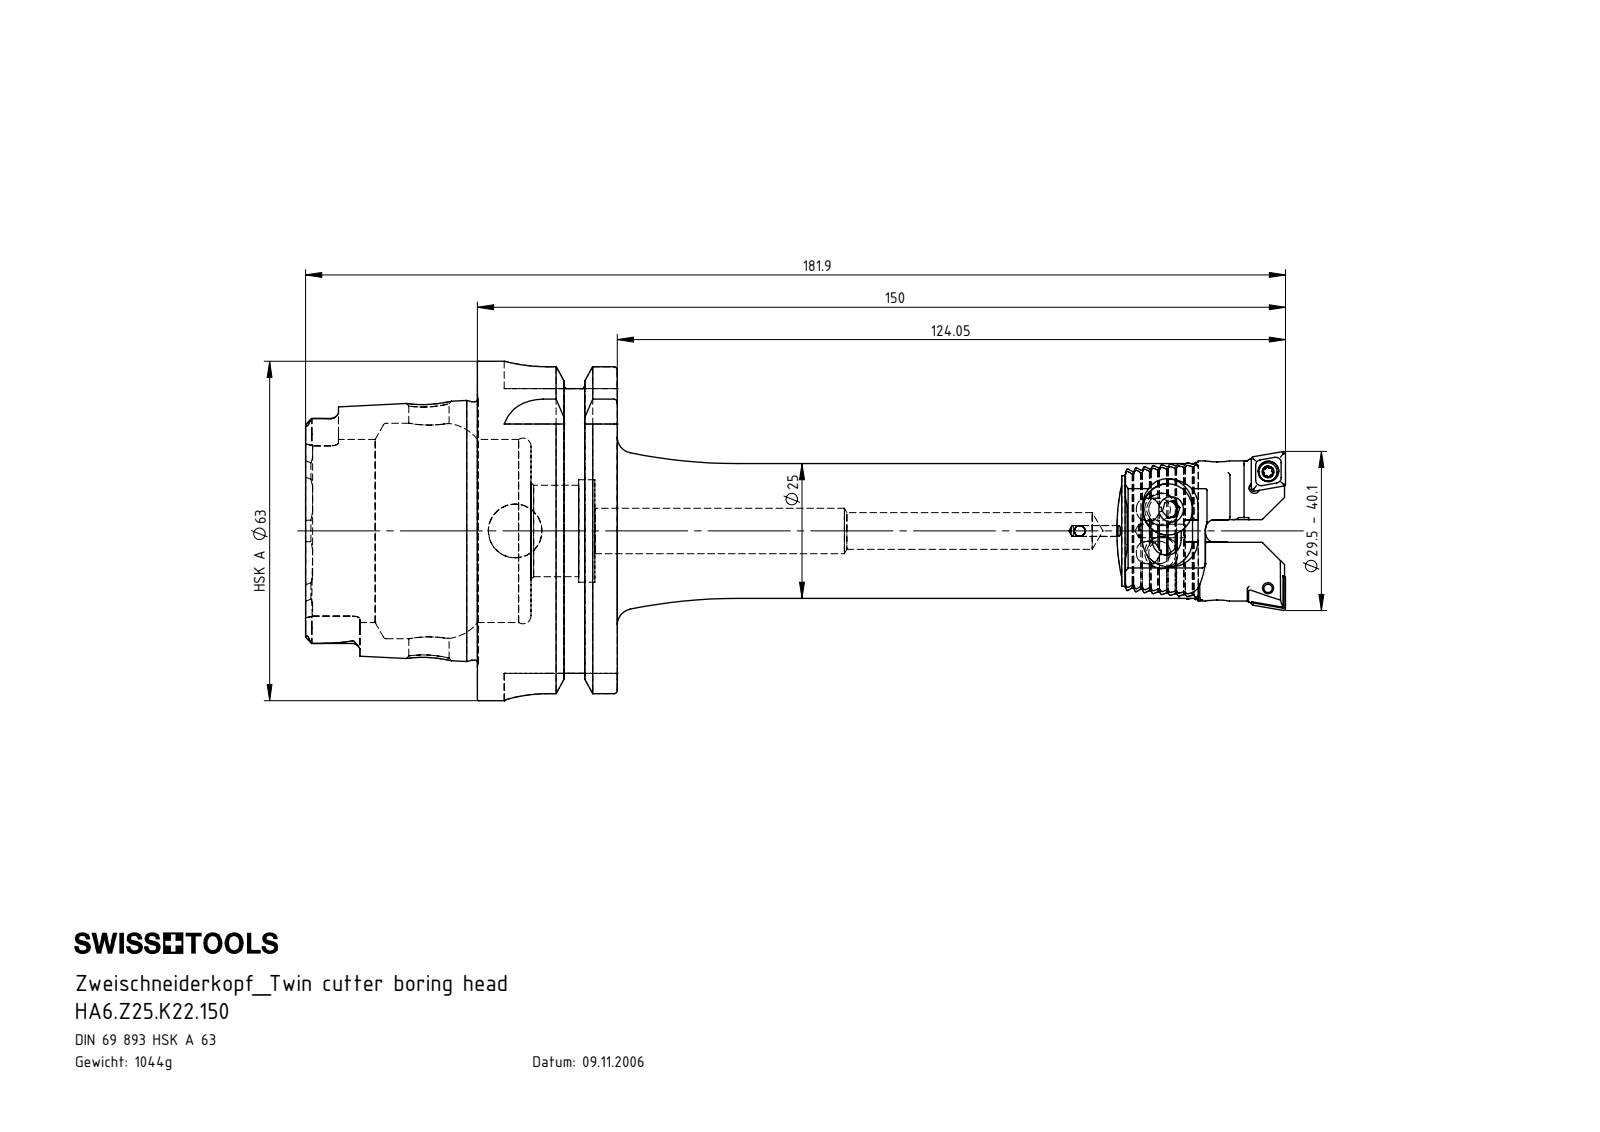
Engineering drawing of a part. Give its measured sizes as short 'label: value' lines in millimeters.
name: CCMT060204; Z25-ER1.003.012_A_gespannt; Z25-ER1.001.012; WCA-ER2.001.006_A (+7 more)
written by: SolidWorks 2022 (CONFIG_CONTROL_DESIGN)
unit: mm
bodies: 14 solids, 1092 faces (502 planar, 281 cylindrical, 309 other)
size: 181.9 × 63 × 63
volume: 133 620 mm³; area: 39 078 mm²
holes: 5× ⌀2, 2× ⌀1.6, 2× ⌀2.05, 2× ⌀2.8, 2× ⌀3.85, 2× ⌀4.2, 2× ⌀5.3, 2× ⌀6, 1× ⌀2.5, 1× ⌀3.5, 1× ⌀6.8, 1× ⌀7.5
bosses: 2× ⌀9.5, 2× ⌀9.2, 2× ⌀5, 2× ⌀3.4, 2× ⌀2.5, 1× ⌀63, 1× ⌀54.95, 1× ⌀47.94
rounds: 18× R0.12, 18× R0.5, 16× R0.12, 12× R0.21, 10× R0.36, 6× R1.4, 4× R2, 4× R2.8
face distances: 25.95, 1.43, 16, 2.86, 9.95, 1.39, 4.29, 31.9, 41.85, 57.85
hole spacings: 3.9, 4, 7, 18.02, 18.11, 20.91, 148.31, 13.52
